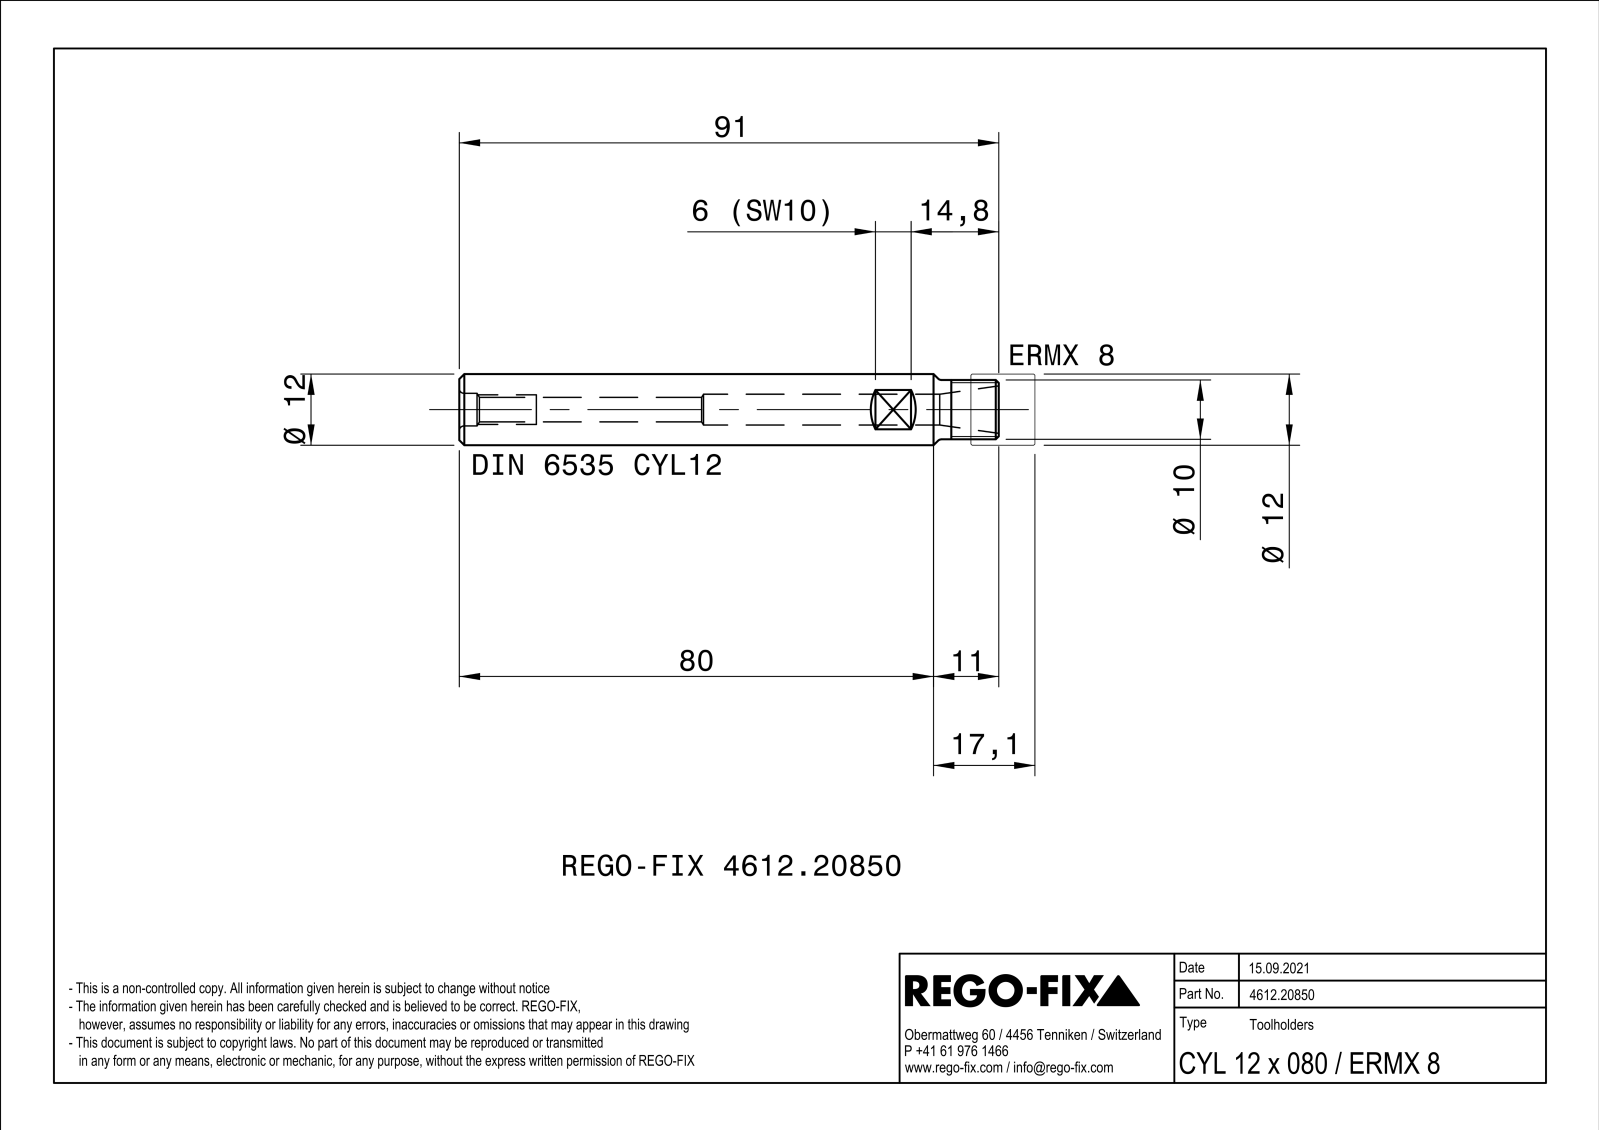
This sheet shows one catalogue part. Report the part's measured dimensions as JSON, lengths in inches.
{"part_name": "NOCUT", "step_written_by": "SIEMENS PLM Software Solid Edge ST10 (AUTOMOTIVE_DESIGN)", "units": "inches", "bodies": {"solids": 1, "faces": 30, "planar": 9, "cylindrical": 9, "other": 12}, "overall_size": [4.213, 0.748, 0.748], "volume_in3": 0.693, "surface_area_in2": 11.4, "round_holes": [[0.163, 1], [0.217, 1], [0.276, 1], [0.413, 1]], "round_bosses_or_shafts": [[0.748, 1], [0.472, 1], [0.457, 1]], "face_to_face_distances": [3.15, 0.669, 1.063, 4.213, 0.153]}
